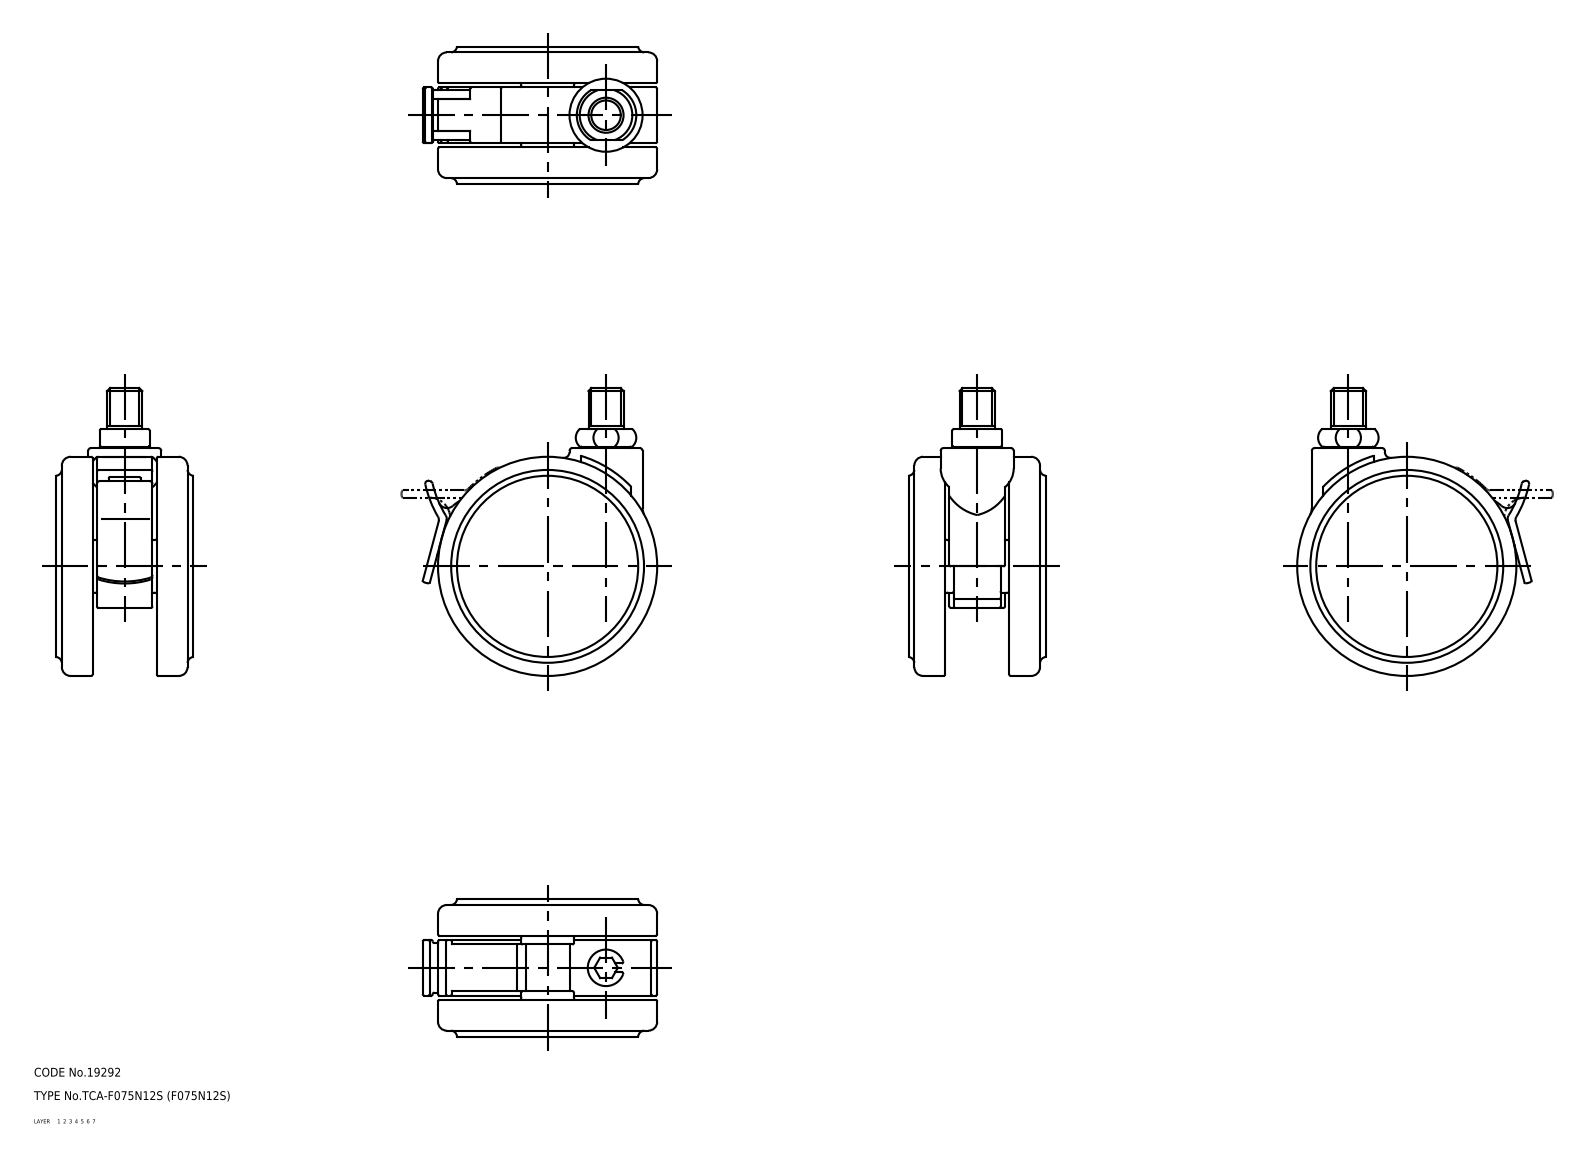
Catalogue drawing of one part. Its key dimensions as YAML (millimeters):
part_name: "67124695; 67124708; 67124721; 67124734 (+1 more)"
step_written_by: "CADfix (AUTOMOTIVE_DESIGN)"
units: millimeters
bodies: {solids: 5, faces: 260, planar: 0, cylindrical: 0, other: 260}
overall_size: [98.5, 80.25, 47]
volume: 156171
surface_area: 39614
